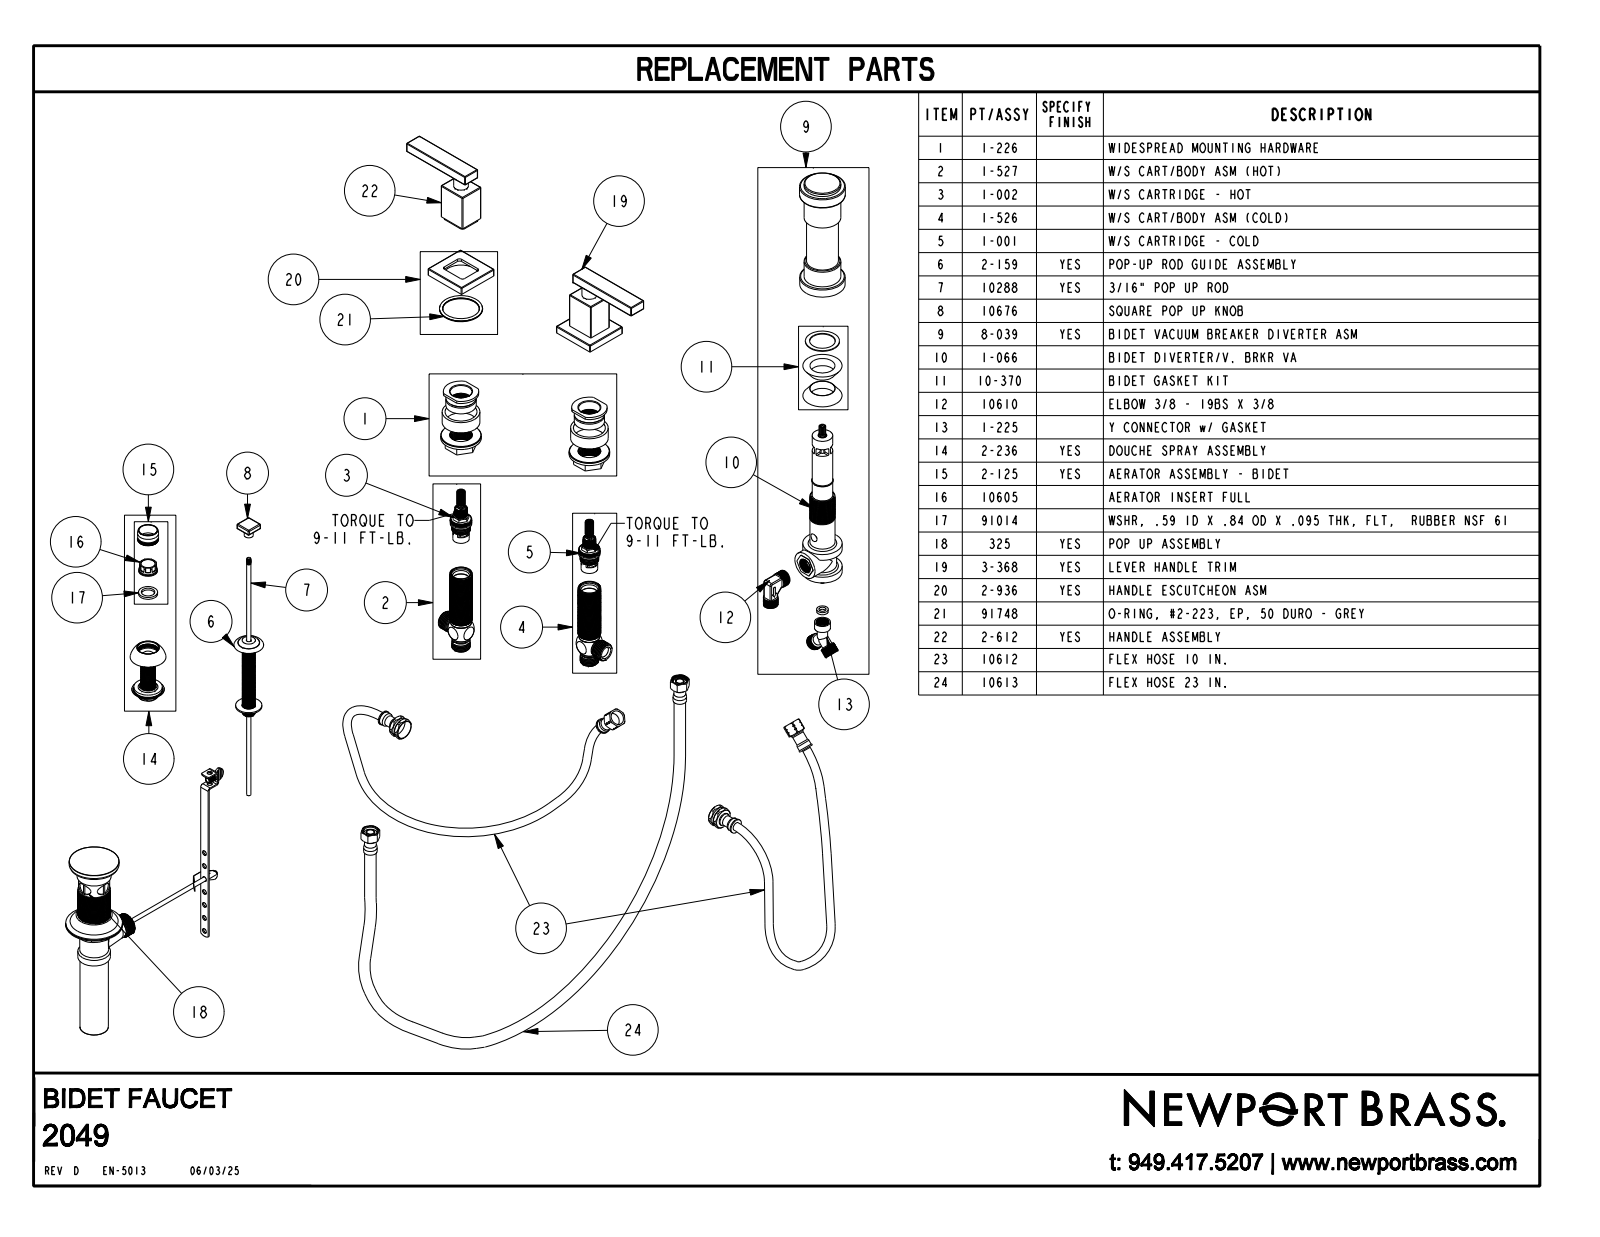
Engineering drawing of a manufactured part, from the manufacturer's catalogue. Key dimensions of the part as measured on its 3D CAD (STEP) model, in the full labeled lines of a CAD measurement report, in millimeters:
Part name (STEP PRODUCT): 2049
STEP written by: CREO PARAMETRIC BY PTC INC, 2018400 (CONFIG_CONTROL_DESIGN)
Units: millimetres
Bodies: 5 solids, 279 faces (85 planar, 112 cylindrical, 82 other)
Overall size (bounding box): 579.1 × 355.6 × 138.3
Volume: 383 100 mm³ · Surface area: 70 320 mm²
Round holes (diameter × count): ⌀15.9 ×1, ⌀20.1 ×1, ⌀23.9 ×1
Round bosses / shafts (diameter × count): ⌀16.5 ×2, ⌀13.3 ×2, ⌀51.3 ×1, ⌀50.8 ×1, ⌀41.1 ×1, ⌀35.6 ×1, ⌀23.5 ×1, ⌀19.7 ×1
Partial cylindrical surfaces — rounded edges, fillets, slot ends (radius × count): R0.8 ×48, R1 ×12, R9.1 ×1
Main face-to-face distances: 4.6, 24.9, 77.5, 8.9, 203.2, 68.6, 66, 57.2, 11.4, 29.5
